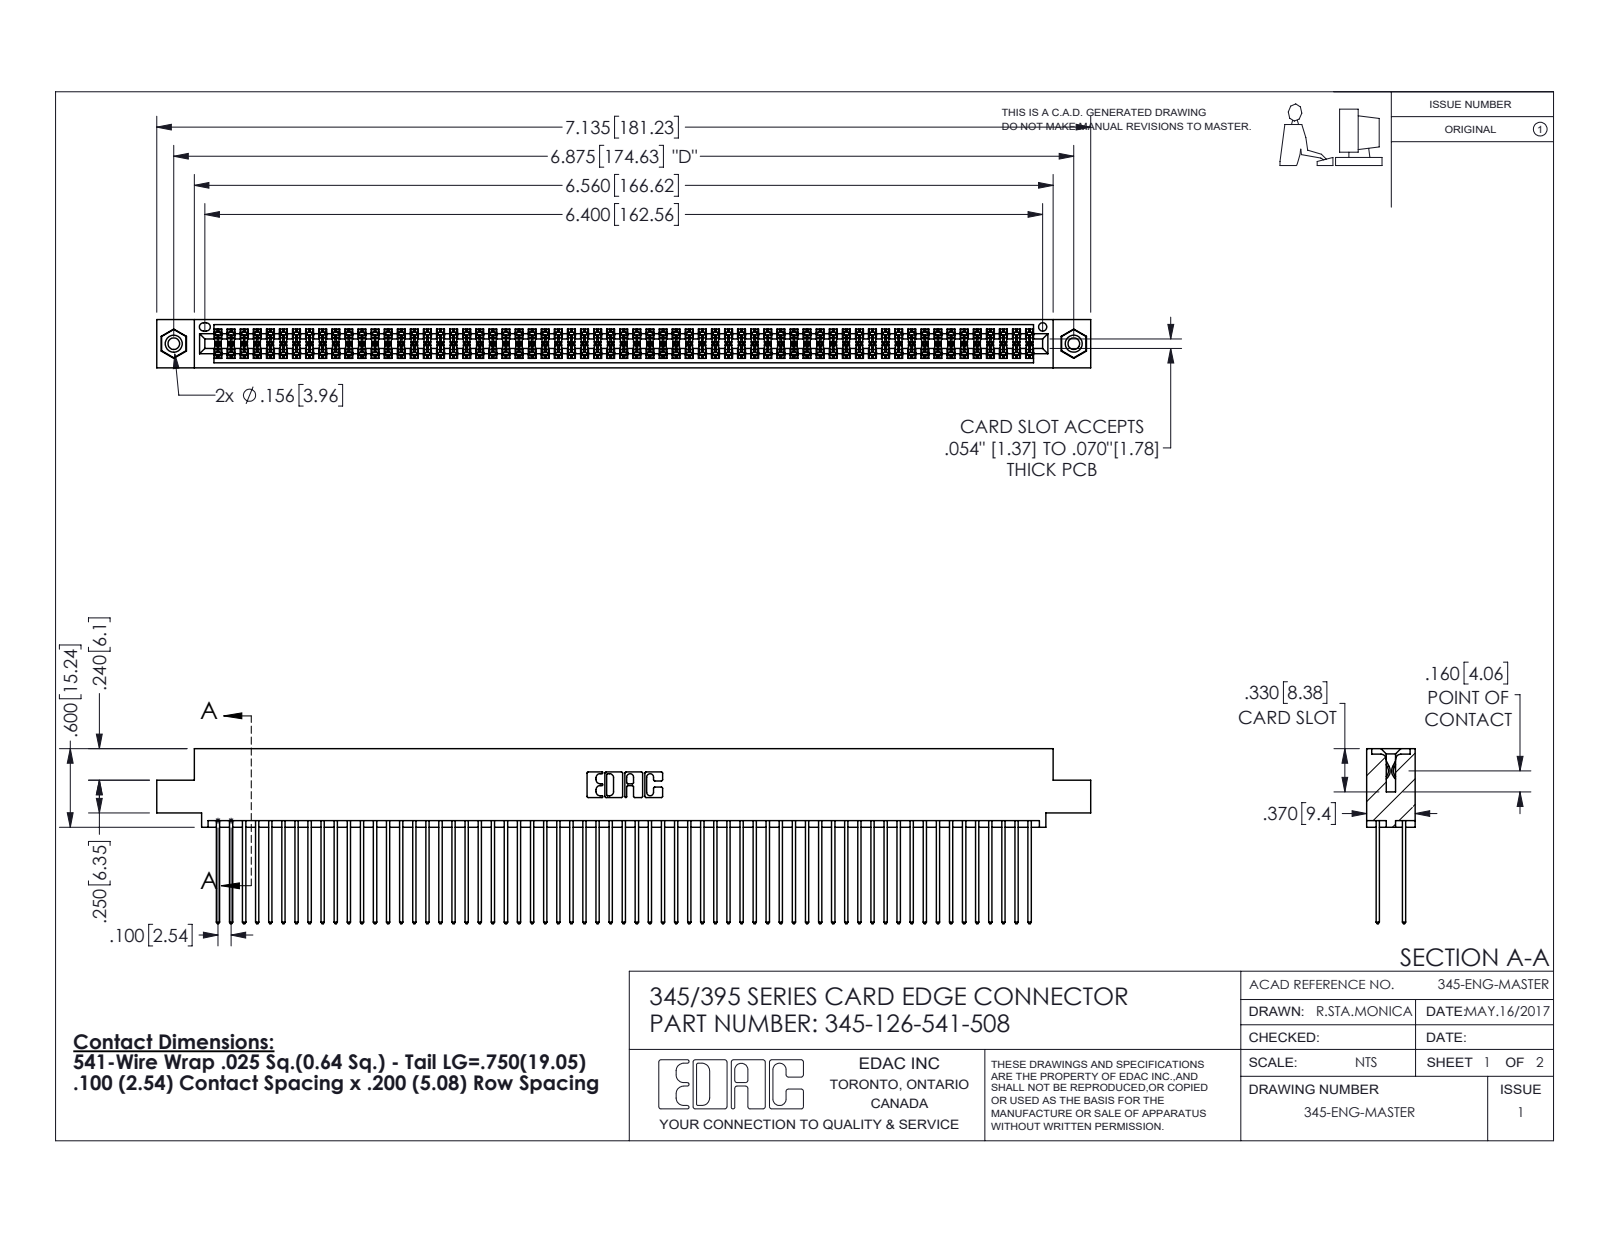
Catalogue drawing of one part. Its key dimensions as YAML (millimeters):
part_name: "345-126-541-508; 345 Part_0.110 Offset - 0.156 Dia-TI; 345-292-001_345-293-141; 345-250-001_345-250-003-102"
step_written_by: "SolidWorks 2016 (CONFIG_CONTROL_DESIGN)"
units: millimeters
bodies: {solids: 129, faces: 6490, planar: 4274, cylindrical: 2200, other: 16}
overall_size: [181.2, 34, 9.4]
volume: 18440
surface_area: 31170
round_holes:
  - {diameter: 2.3, count: 2}
  - {diameter: 3.2, count: 2}
  - {diameter: 4, count: 2}
  - {diameter: 1.6, count: 1}
round_bosses_or_shafts:
  - {diameter: 3.9, count: 2}
partial_cylinders:
  - {radius: 0.2, count: 189}
  - {radius: 0.3, count: 126}
  - {radius: 0.3, count: 22}
  - {radius: 0.2, count: 6}
  - {radius: 0.8, count: 6}
  - {radius: 0.7, count: 3}
  - {radius: 0.4, count: 2}
  - {radius: 0.5, count: 2}
face_to_face_distances: [1.8, 7.6, 5.1, 2.5, 6.9, 0.6, 5.7, 9.4, 4.4, 3.8]
hole_center_spacings: [6.9, 168.6, 174.6]
